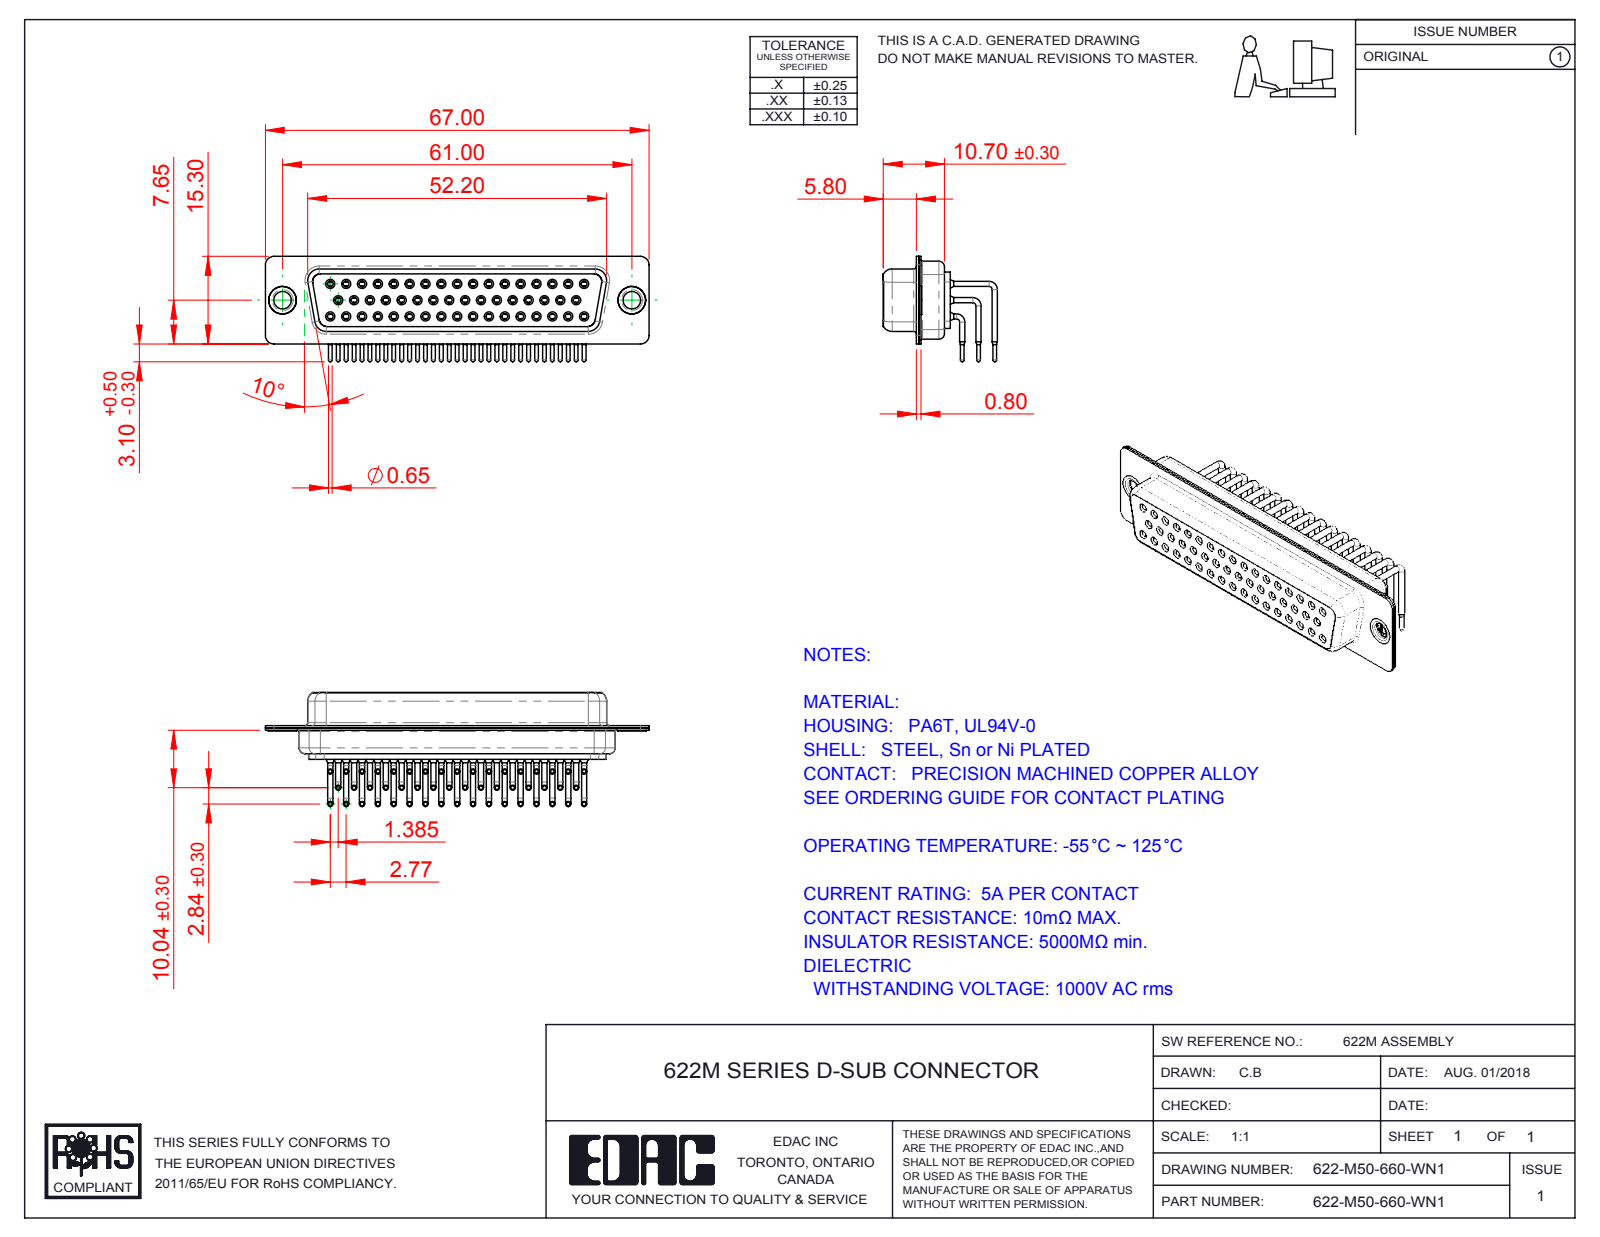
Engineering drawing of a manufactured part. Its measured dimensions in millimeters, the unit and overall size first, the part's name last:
Units: millimetres
Overall size (bounding box): 67 × 19.93 × 18.4
Round holes (diameter × count): ⌀1 ×50, ⌀1.1 ×50, ⌀1.7 ×50, ⌀1.8 ×50, ⌀2 ×50, ⌀3.05 ×2, ⌀4 ×2, ⌀4.8 ×2
Round bosses / shafts (diameter × count): ⌀0.9 ×100, ⌀1.6 ×50, ⌀1.5 ×50, ⌀0.65 ×50, ⌀5 ×2, ⌀4.9 ×2, ⌀3.55 ×2
Partial cylindrical surfaces — rounded edges, fillets, slot ends (radius × count): R1.5 ×16, R2 ×12, R1.35 ×8, R1.6 ×8, R0.25 ×4, R0.5 ×4, R0.6 ×4, R0.65 ×4
Main face-to-face distances: 0.4, 1.35, 11.85, 0.85, 2.2, 5.5, 12.25, 5.9, 10.5, 10.05
Hole centre spacings: 2.77, 3.16, 5.54, 8.31, 11.08, 13.85, 16.62, 19.39
Volume: 6 854 mm³ · Surface area: 15 982 mm²
Bodies: 55 solids, 2903 faces (817 planar, 1271 cylindrical, 815 other)
Part name (STEP PRODUCT): 622M Contact Row 1_50 Contacts; 622M Housing_50 Contacts; 622M Thru Hole Rivet; 622-M50-660-WN1 (+4 more)
STEP written by: SolidWorks 2016 (CONFIG_CONTROL_DESIGN)
